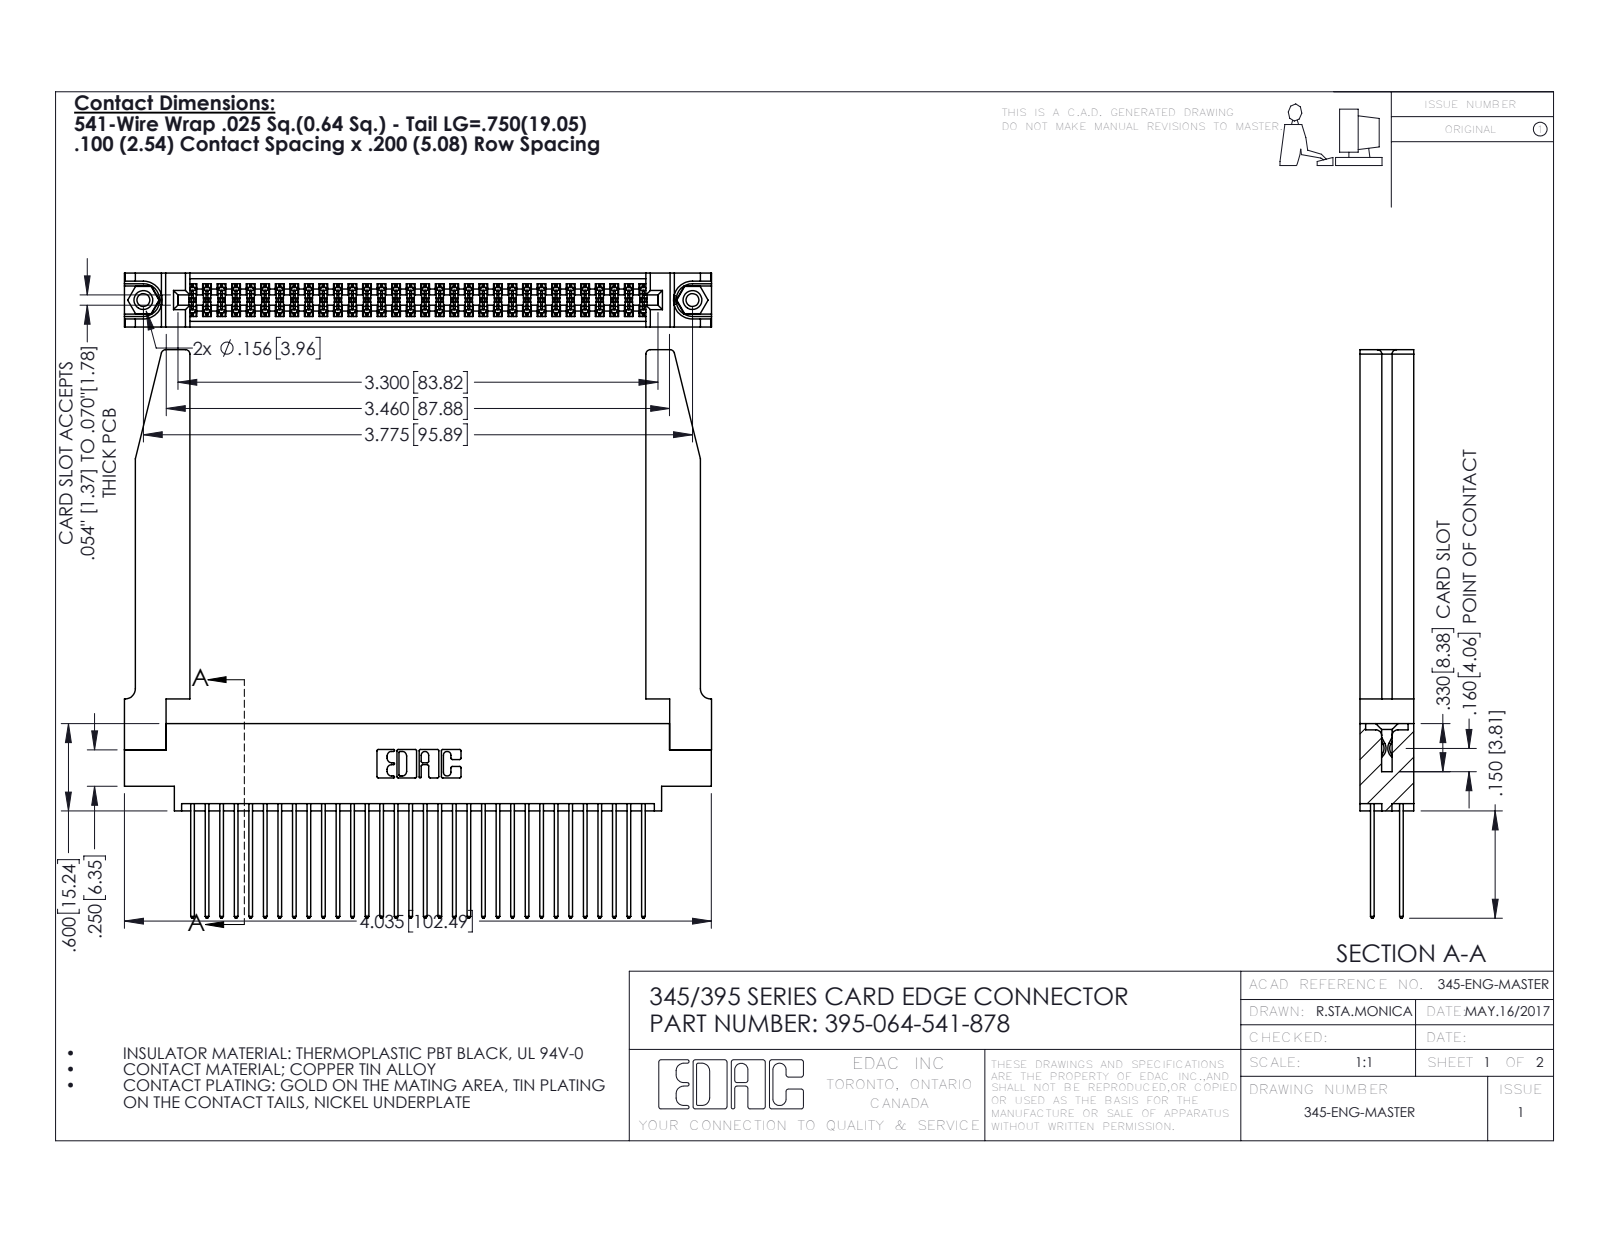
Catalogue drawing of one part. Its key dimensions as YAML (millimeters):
part_name: "345 Part_0.170 Offset - 0.156 Dia-TH; 345-250-001_345-250-001-102; 345-220-078_345-220-078; 395-064-541-878 (+1 more)"
step_written_by: "SolidWorks 2016 (CONFIG_CONTROL_DESIGN)"
units: millimeters
bodies: {solids: 69, faces: 3564, planar: 2338, cylindrical: 1174, other: 52}
overall_size: [102.5, 99.2, 9.4]
volume: 17890
surface_area: 23470
round_holes:
  - {diameter: 2.3, count: 2}
  - {diameter: 3.2, count: 2}
  - {diameter: 4, count: 2}
  - {diameter: 1.6, count: 1}
round_bosses_or_shafts:
  - {diameter: 3.9, count: 2}
partial_cylinders:
  - {radius: 0.2, count: 96}
  - {radius: 0.3, count: 64}
  - {radius: 0.3, count: 22}
  - {radius: 0.8, count: 8}
  - {radius: 0.2, count: 6}
  - {radius: 0.8, count: 6}
  - {radius: 0.7, count: 3}
  - {radius: 0.4, count: 2}
face_to_face_distances: [1.8, 9.4, 7.6, 2.5, 6.9, 0.6, 5.1, 5.7, 4.4, 3.8]
hole_center_spacings: [6.9, 89.9, 95.9]
